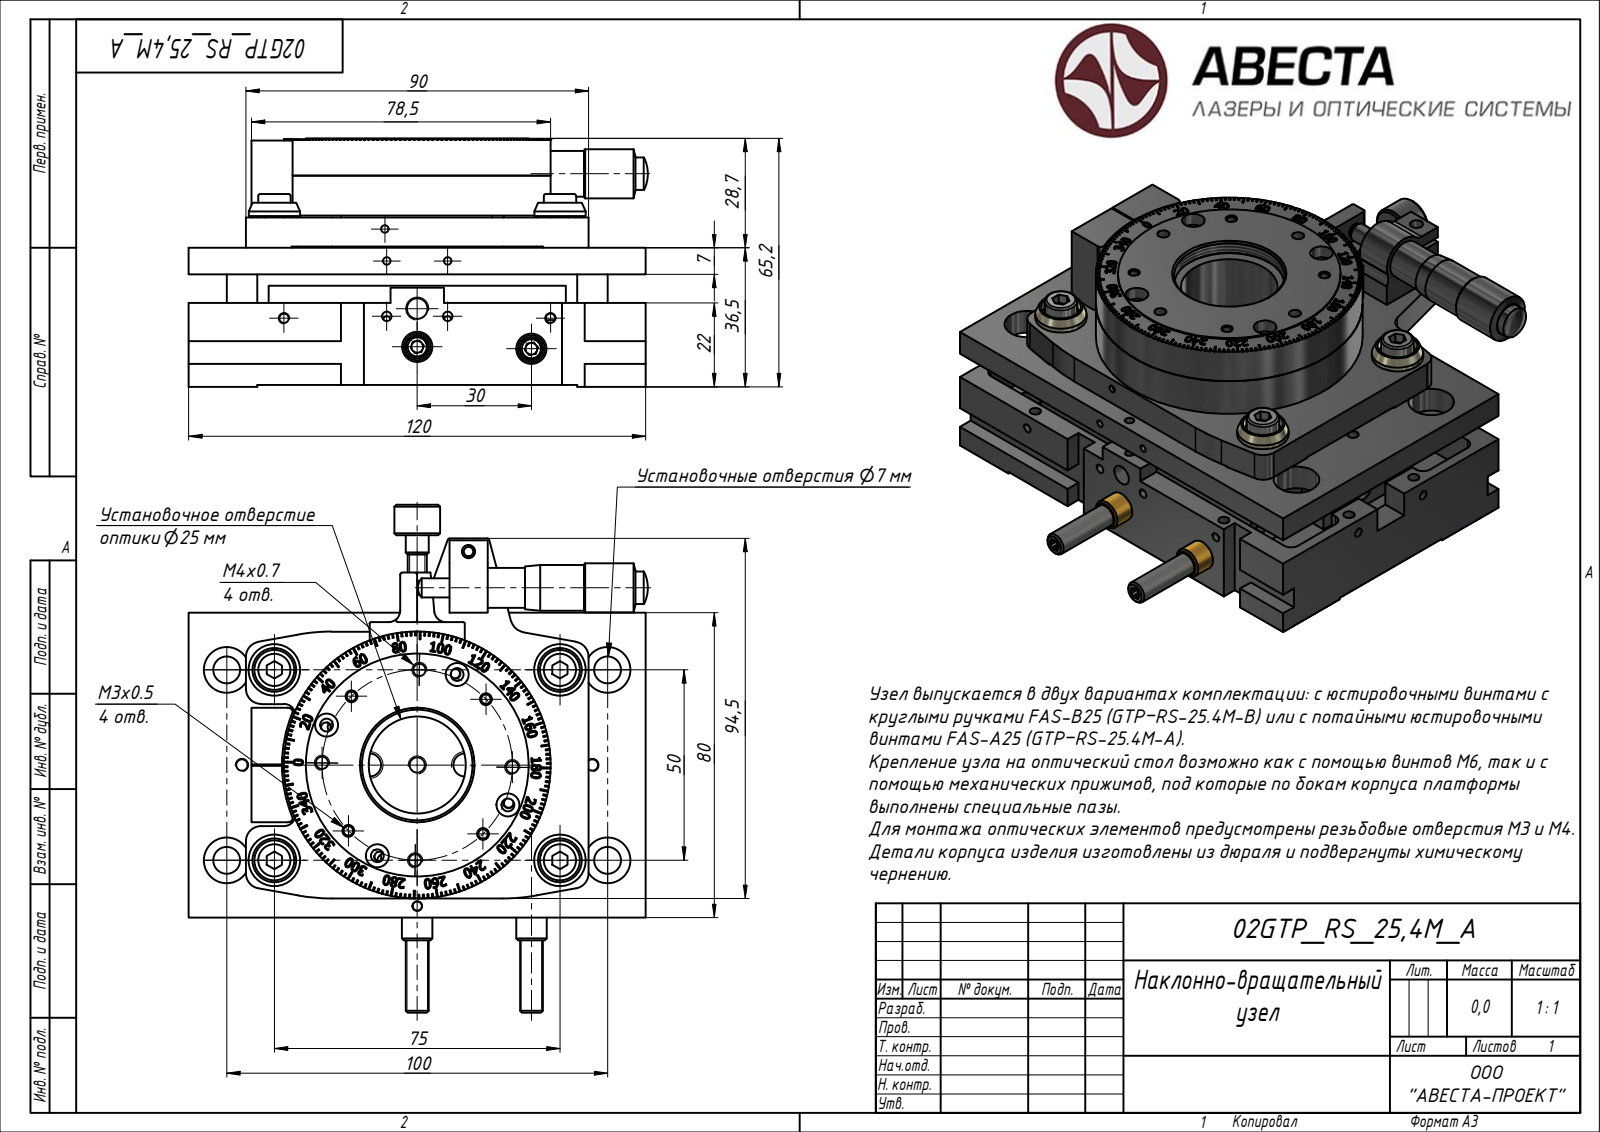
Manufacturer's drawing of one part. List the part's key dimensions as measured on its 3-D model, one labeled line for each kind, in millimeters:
Part name (STEP PRODUCT): Block 01; Block 02; Block 03; Block 04 (+3 more)
STEP written by: ST-DEVELOPER v15 (AUTOMOTIVE_DESIGN)
Units: millimetres
Bodies: 16 solids, 2803 faces (0 planar, 0 cylindrical, 2803 other)
Overall size (bounding box): 133.3 × 120.5 × 65.2
Volume: 45 358 mm³ · Surface area: 127 577 mm²
